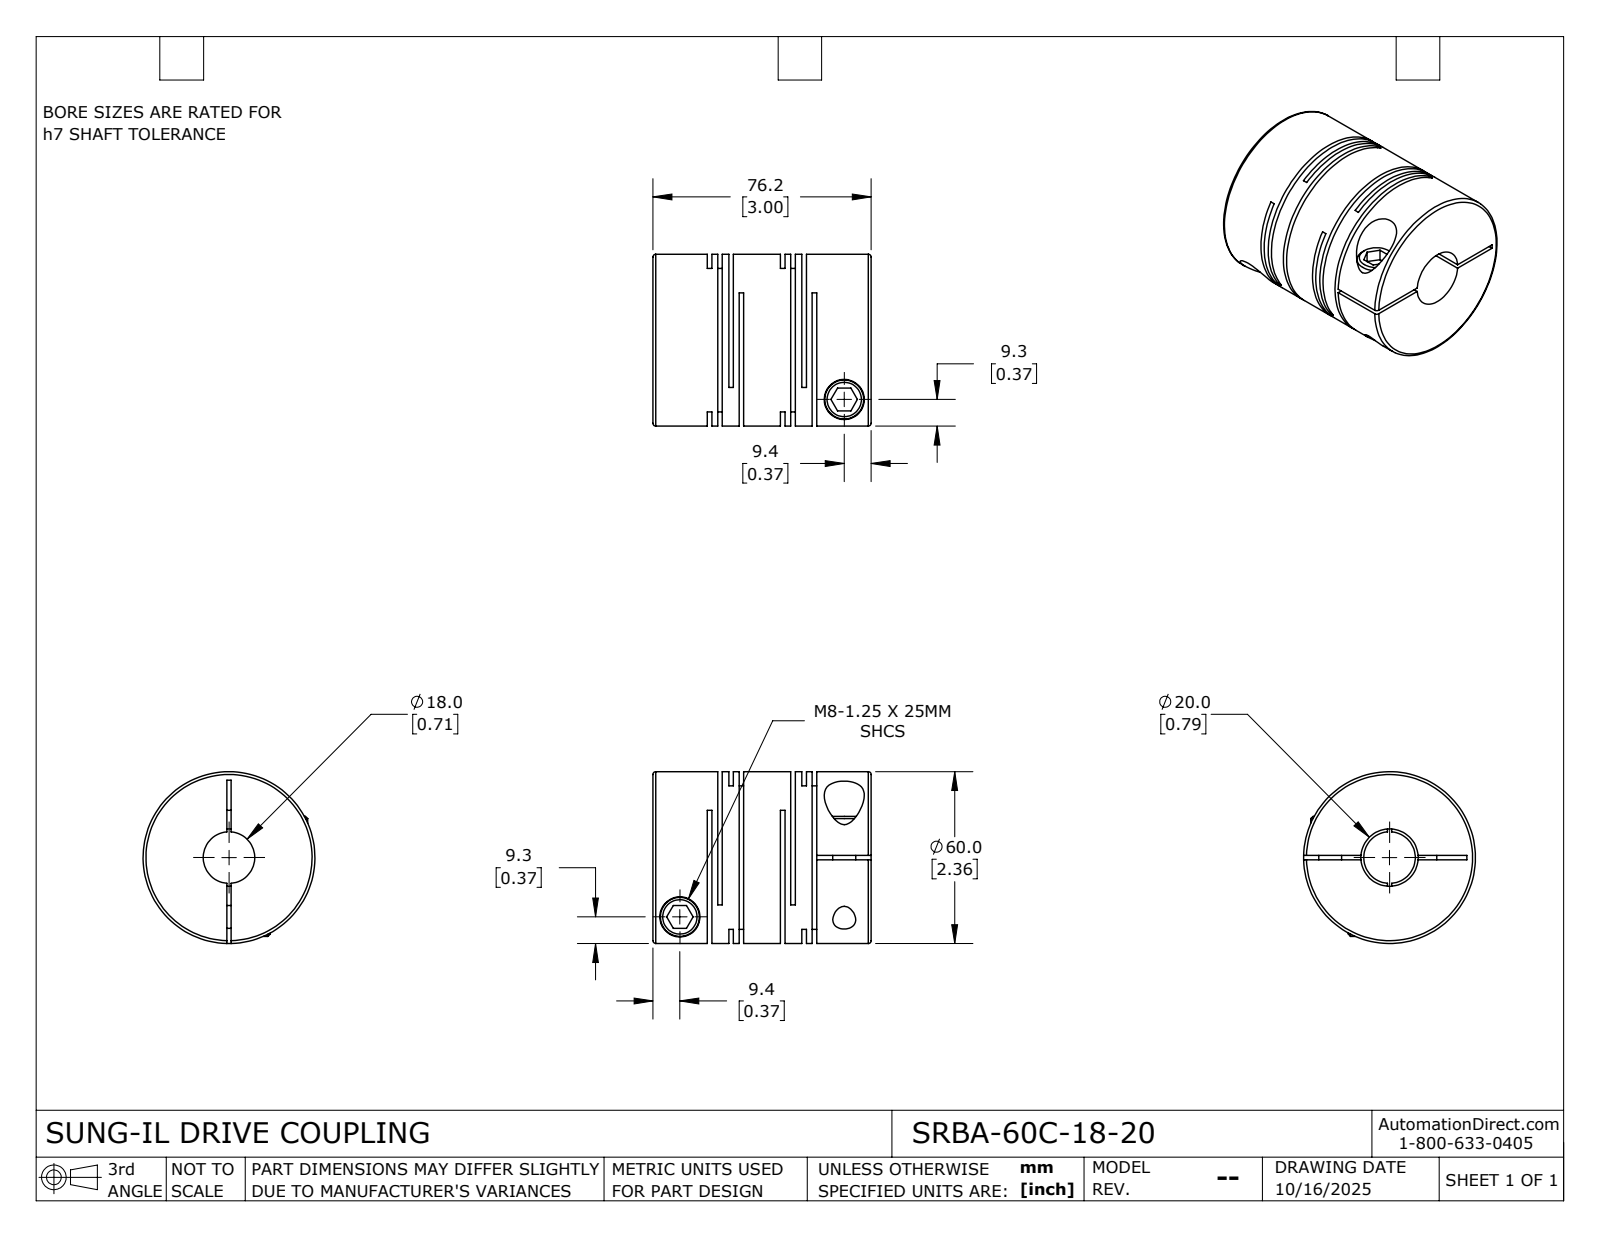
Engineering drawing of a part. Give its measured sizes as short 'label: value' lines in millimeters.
name: SRBA-60C-18-20
written by: SolidWorks 2024 (CONFIG_CONTROL_DESIGN)
unit: mm
bodies: 1 solid, 115 faces (60 planar, 42 cylindrical, 13 other)
size: 76.2 × 60 × 60
volume: 161 355 mm³; area: 59 191 mm²
holes: 2× ⌀8, 2× ⌀14, 1× ⌀18, 1× ⌀20
bosses: 2× ⌀13.6, 1× ⌀60
face distances: 1.6, 3.6, 7.5, 25.5, 33, 2, 5.9, 23.9, 3.9, 18
